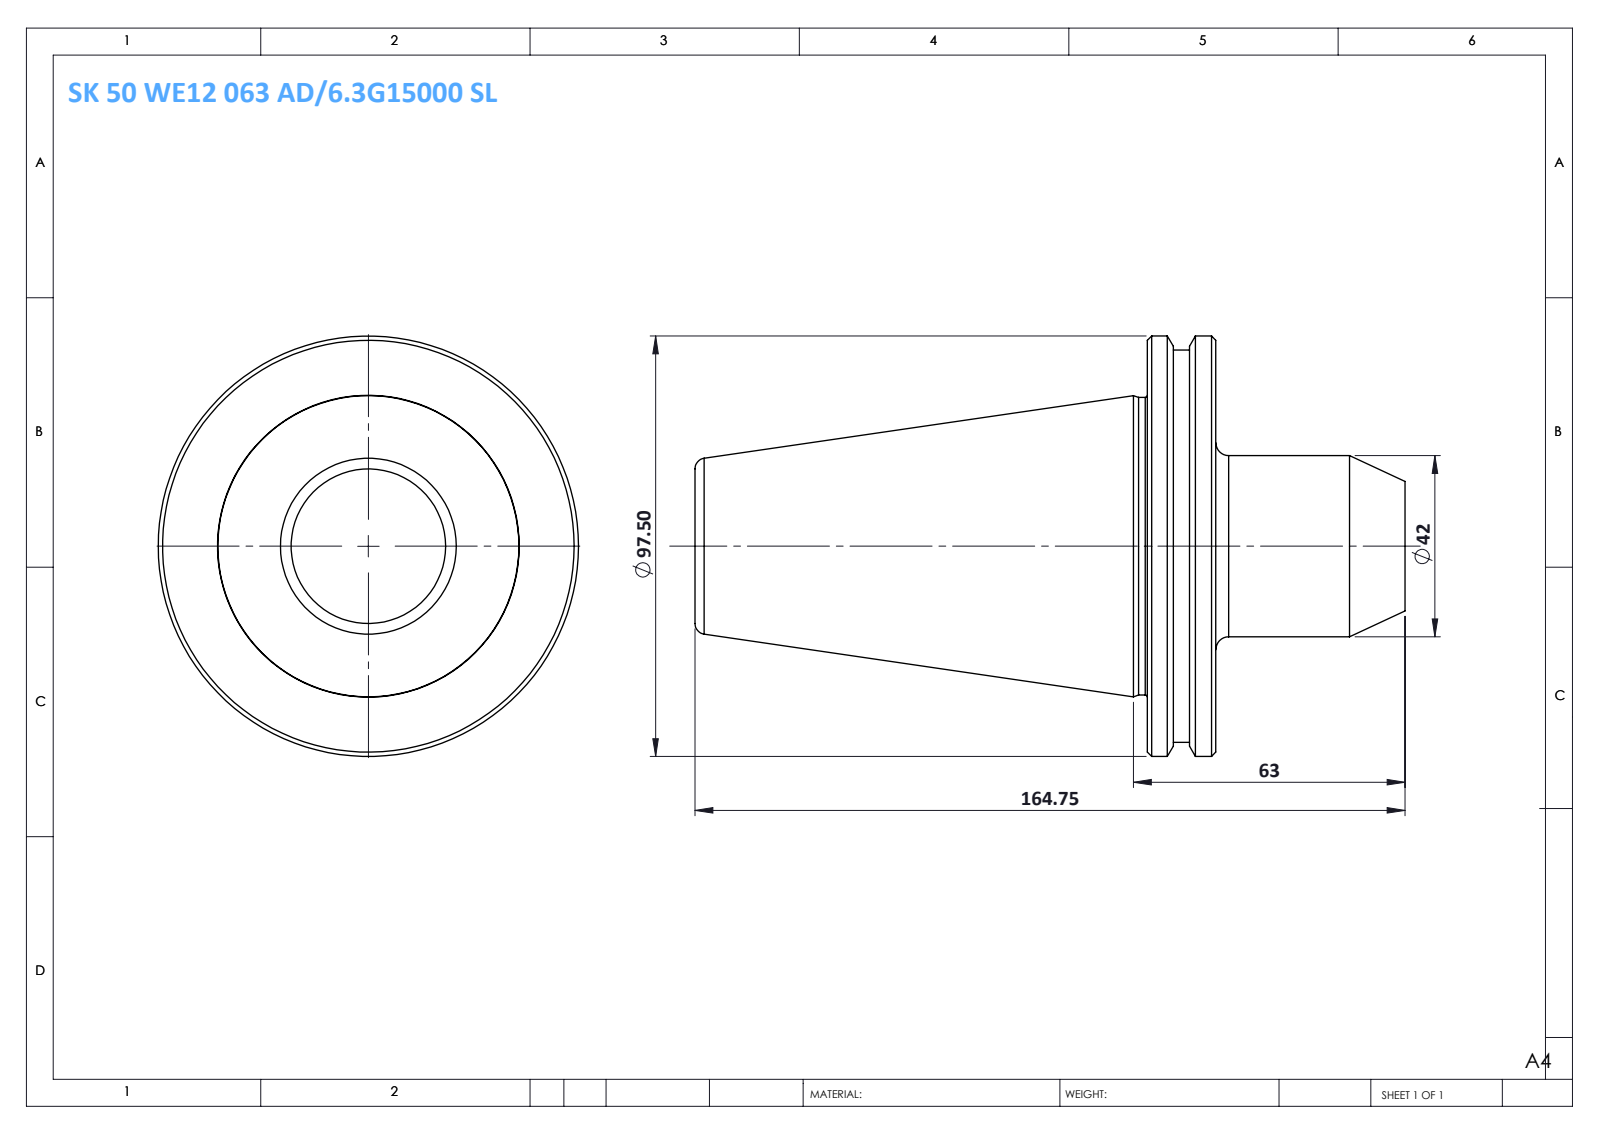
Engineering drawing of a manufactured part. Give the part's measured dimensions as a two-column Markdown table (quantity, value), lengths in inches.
| quantity | value |
| --- | --- |
| part name | SK50 WE12 063 AD-6.3G15000 SL |
| STEP written by | SolidWorks 2014 (CONFIG_CONTROL_DESIGN) |
| units | inches |
| bodies | 1 solid, 36 faces (6 planar, 10 cylindrical, 20 other) |
| overall size | 6.486 × 3.839 × 3.839 |
| volume | 26.23 in³ |
| surface area | 64.15 in² |
| round bosses / shafts (diameter × count) | 3.839 × 1, 3.583 × 1, 2.717 × 1, 1.654 × 1 |
| main face-to-face distances | 0.626, 4.758, 4.132, 1.728, 2.354, 6.486, 1.969, 0.241, 0.385, 4.517 |
